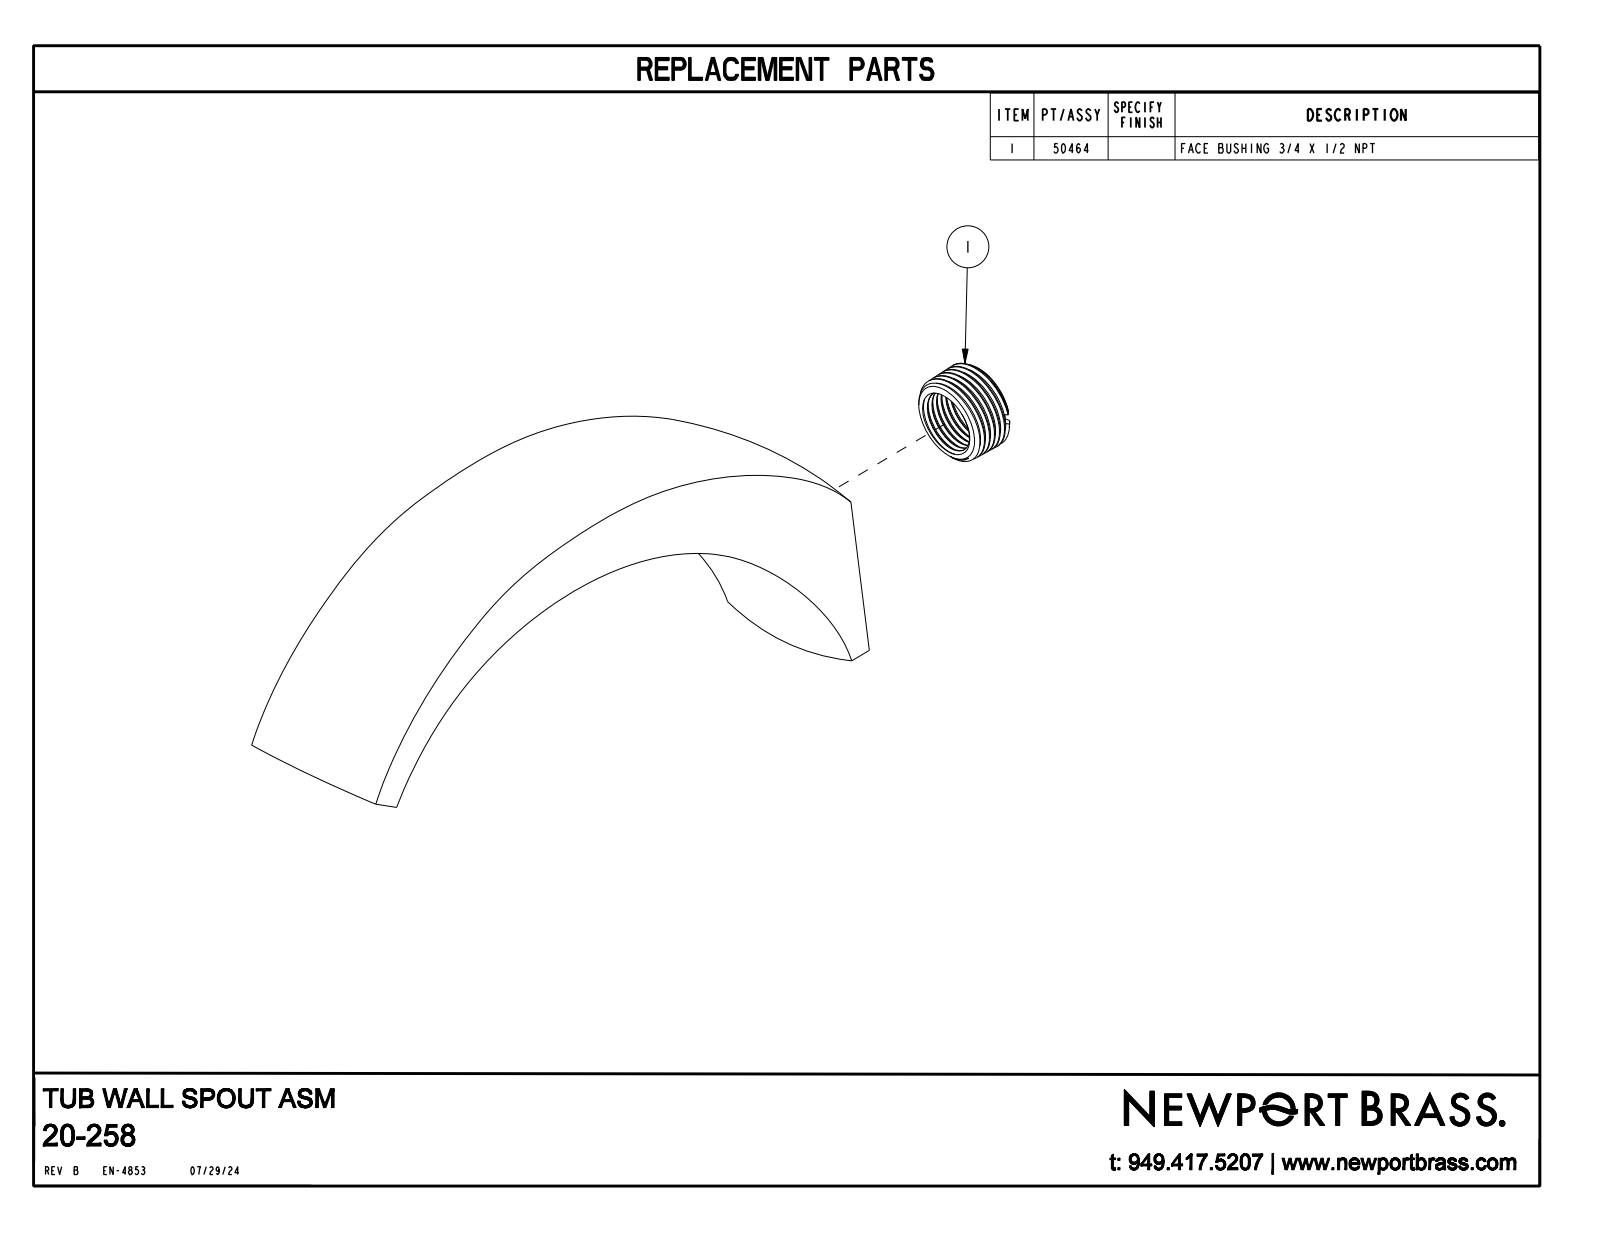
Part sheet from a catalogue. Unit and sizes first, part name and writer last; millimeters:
Units: millimetres
Overall size (bounding box): 186.7 × 94.3 × 50.8
Partial cylindrical surfaces — rounded edges, fillets, slot ends (radius × count): R127 ×1
Main face-to-face distances: 50.8
Volume: 245 000 mm³ · Surface area: 33 590 mm²
Bodies: 1 solid, 7 faces (4 planar, 1 cylindrical, 2 other)
Part name (STEP PRODUCT): 20-258
STEP written by: CREO PARAMETRIC BY PTC INC, 2018400 (AUTOMOTIVE_DESIGN)
